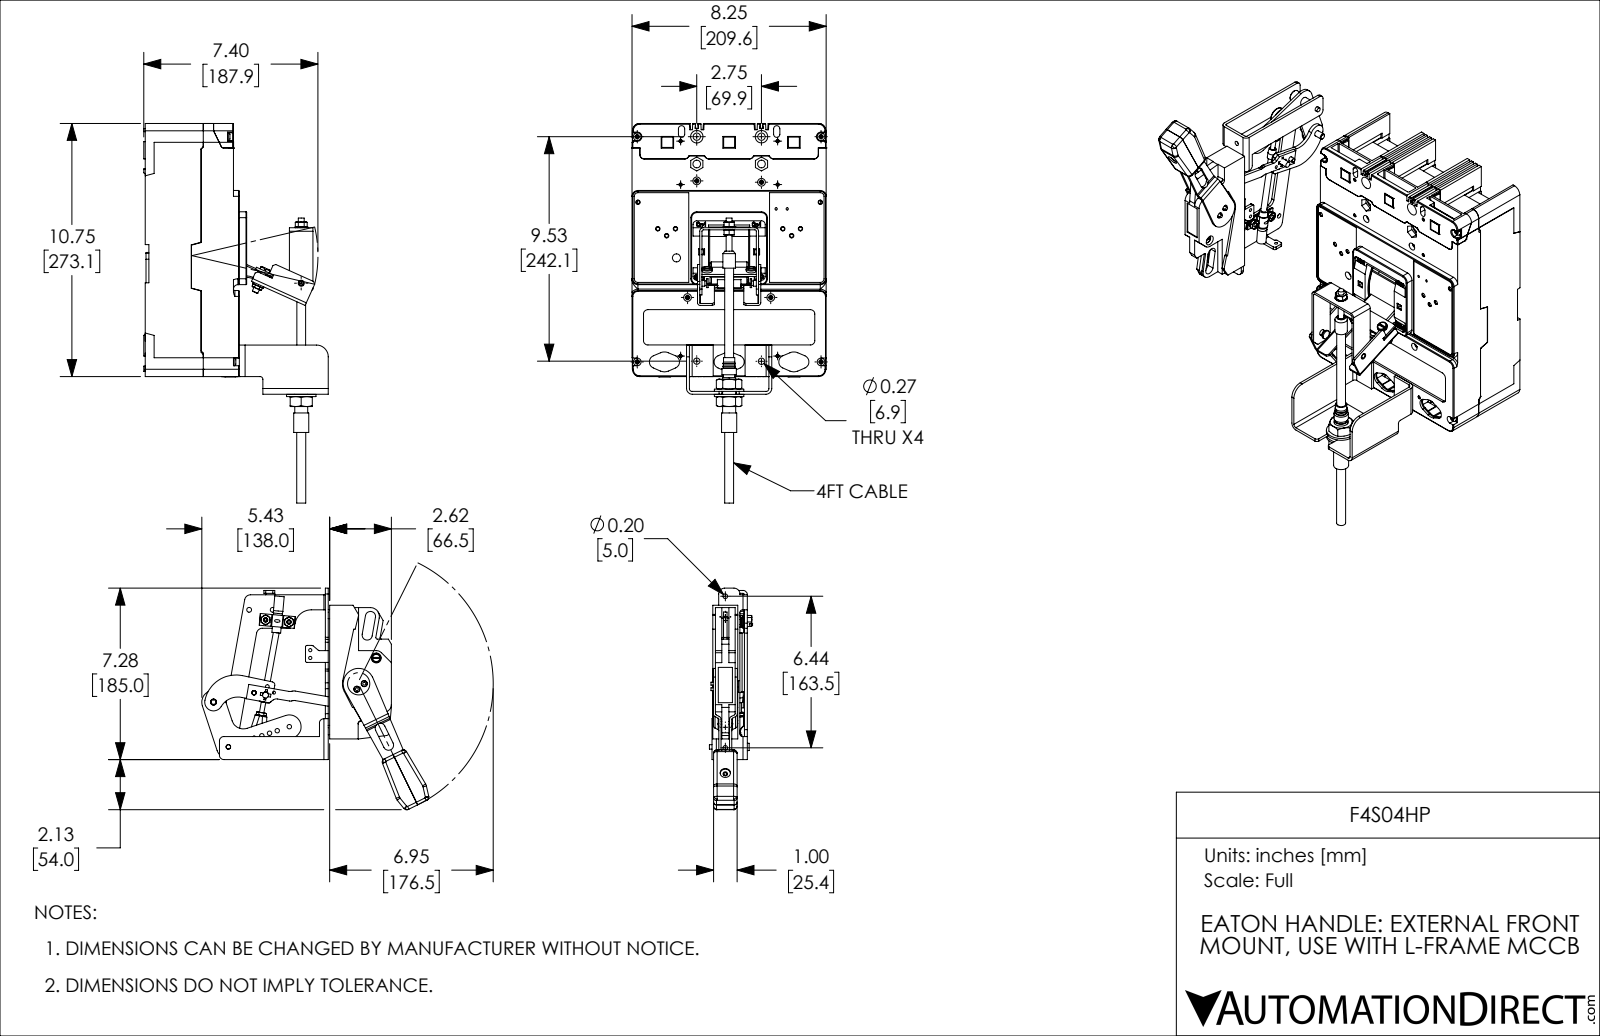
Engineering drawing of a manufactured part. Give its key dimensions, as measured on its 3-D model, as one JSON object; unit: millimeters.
{"part_name": "F4S04HP_HANDLE; F4S04HP; F4S04HP_BREAKER", "step_written_by": "SolidWorks 2019 (CONFIG_CONTROL_DESIGN)", "units": "millimeters", "bodies": {"solids": 97, "faces": 5868, "planar": 4033, "cylindrical": 1439, "other": 396}, "overall_size": [415.5, 365.9, 245.1], "volume_mm3": 3921000, "surface_area_mm2": 767100, "round_holes": [[4.8, 13], [4.3, 10], [3.7, 8], [8.3, 7], [2.8, 6], [3.6, 6], [4.8, 6], [5.2, 6], [13.5, 6], [3.7, 4], [5.5, 4], [6.4, 4]], "round_bosses_or_shafts": [[6.4, 11], [9.5, 6], [7.4, 6], [12.7, 4], [8.3, 3], [7.9, 3], [11.9, 2], [10.8, 2]], "partial_cylinders_radius": [[1.6, 70], [0.8, 53], [6.4, 52], [3.2, 40], [0.8, 32], [4.8, 30], [1.5, 28], [4, 18]], "face_to_face_distances": [61.9, 209.6, 6.4, 94.4, 32.5, 3.2, 69.9, 2.4, 100.8, 38.9], "hole_center_spacings": [134.1, 69.9, 198.5, 134.2, 242.9, 64.3, 243, 64.3]}
